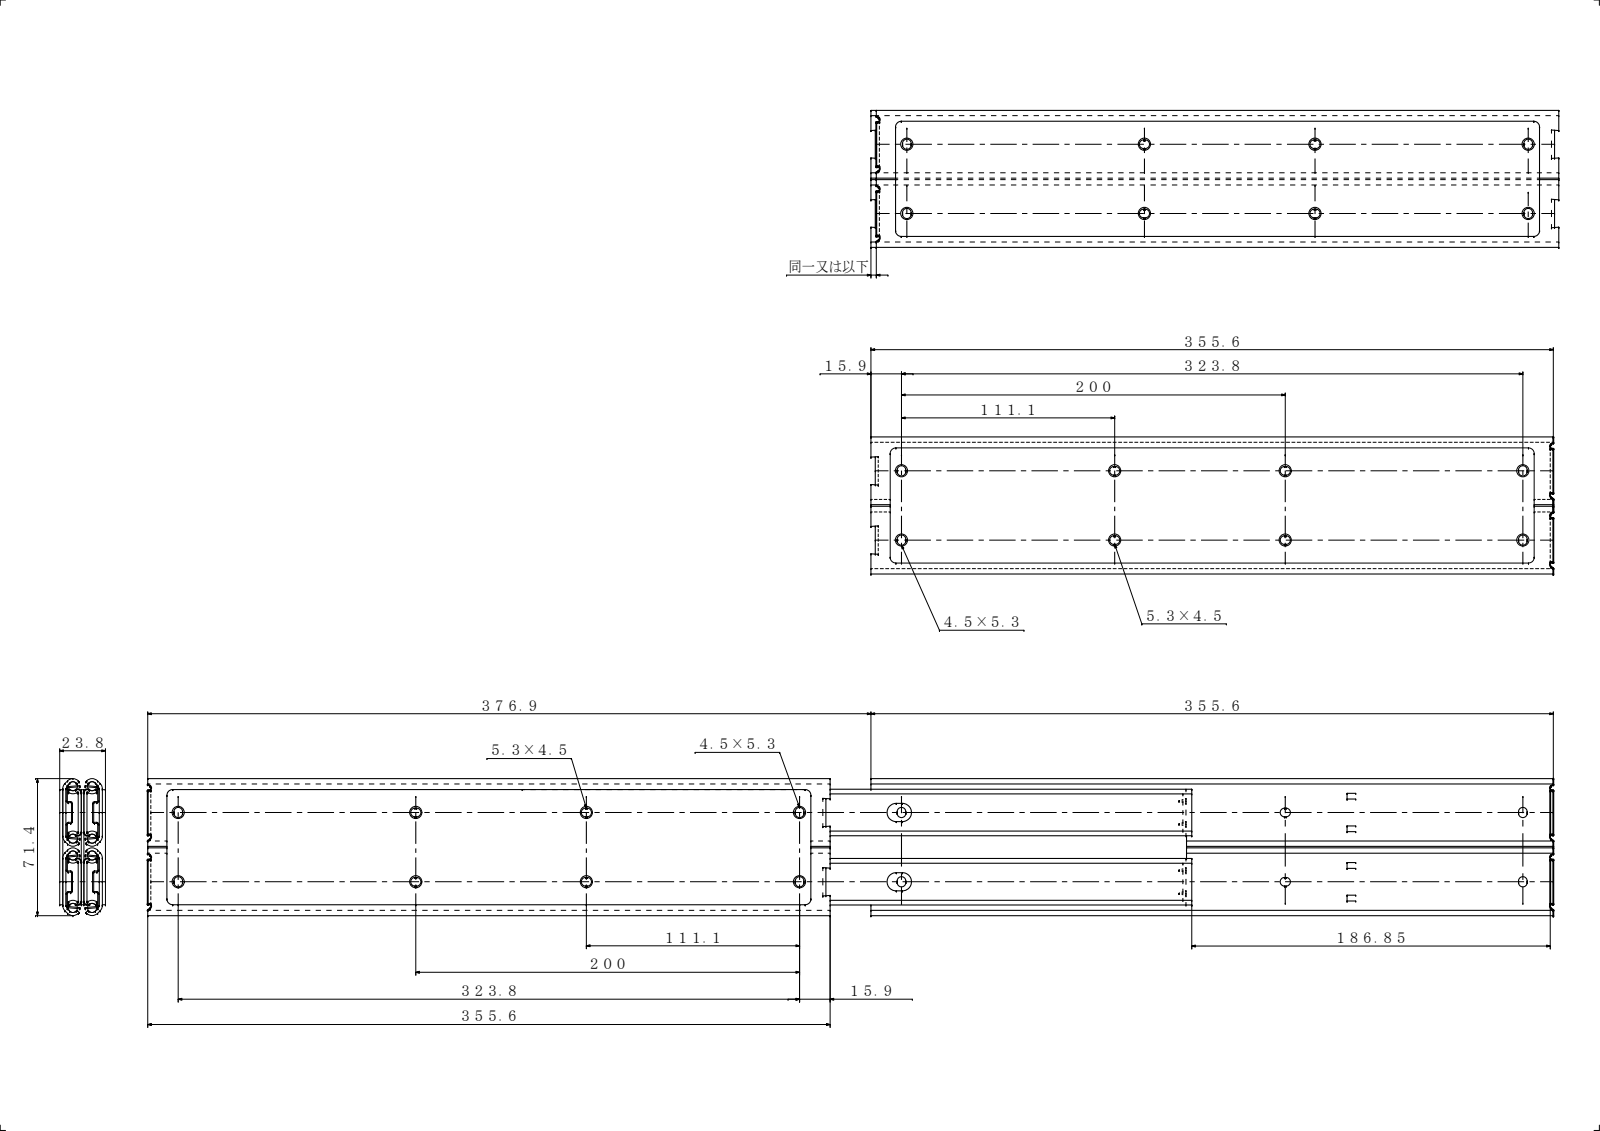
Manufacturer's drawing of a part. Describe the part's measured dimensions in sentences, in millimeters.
The part is named "IM-3551-14; OM-3551-14; 3551-14; IM-14継板 (+1 more)". Its 3-D file was written by "SolidWorks 2019 (CONFIG_CONTROL_DESIGN)". It is 11 solids with 568 faces: 262 planar, 306 cylindrical and 0 other. Overall it measures 732.5 by 71.4 by 23.8 millimeters. Its volume is 270 253 cubic millimeters and its surface area 358 978 square millimeters. Round holes: 20 of diameter 6.4, 2 of diameter 6.5. Partial cylindrical surfaces (rounded edges, fillets, slot ends): 32 of radius 2.25, 24 of radius 0.4, 20 of radius 4, 16 of radius 1, 16 of radius 3, 12 of radius 2, 8 of radius 0.2, 8 of radius 1.8. The main face-to-face distances are 1.6, 11, 9.6, 20.6, 12.6, 8, 11.2, 22.2, 1.4, 3.2. The hole center spacings are 36.1, 50.8, 60.3, 62.32, 70.28, 88.9, 95.95, 111.1.
